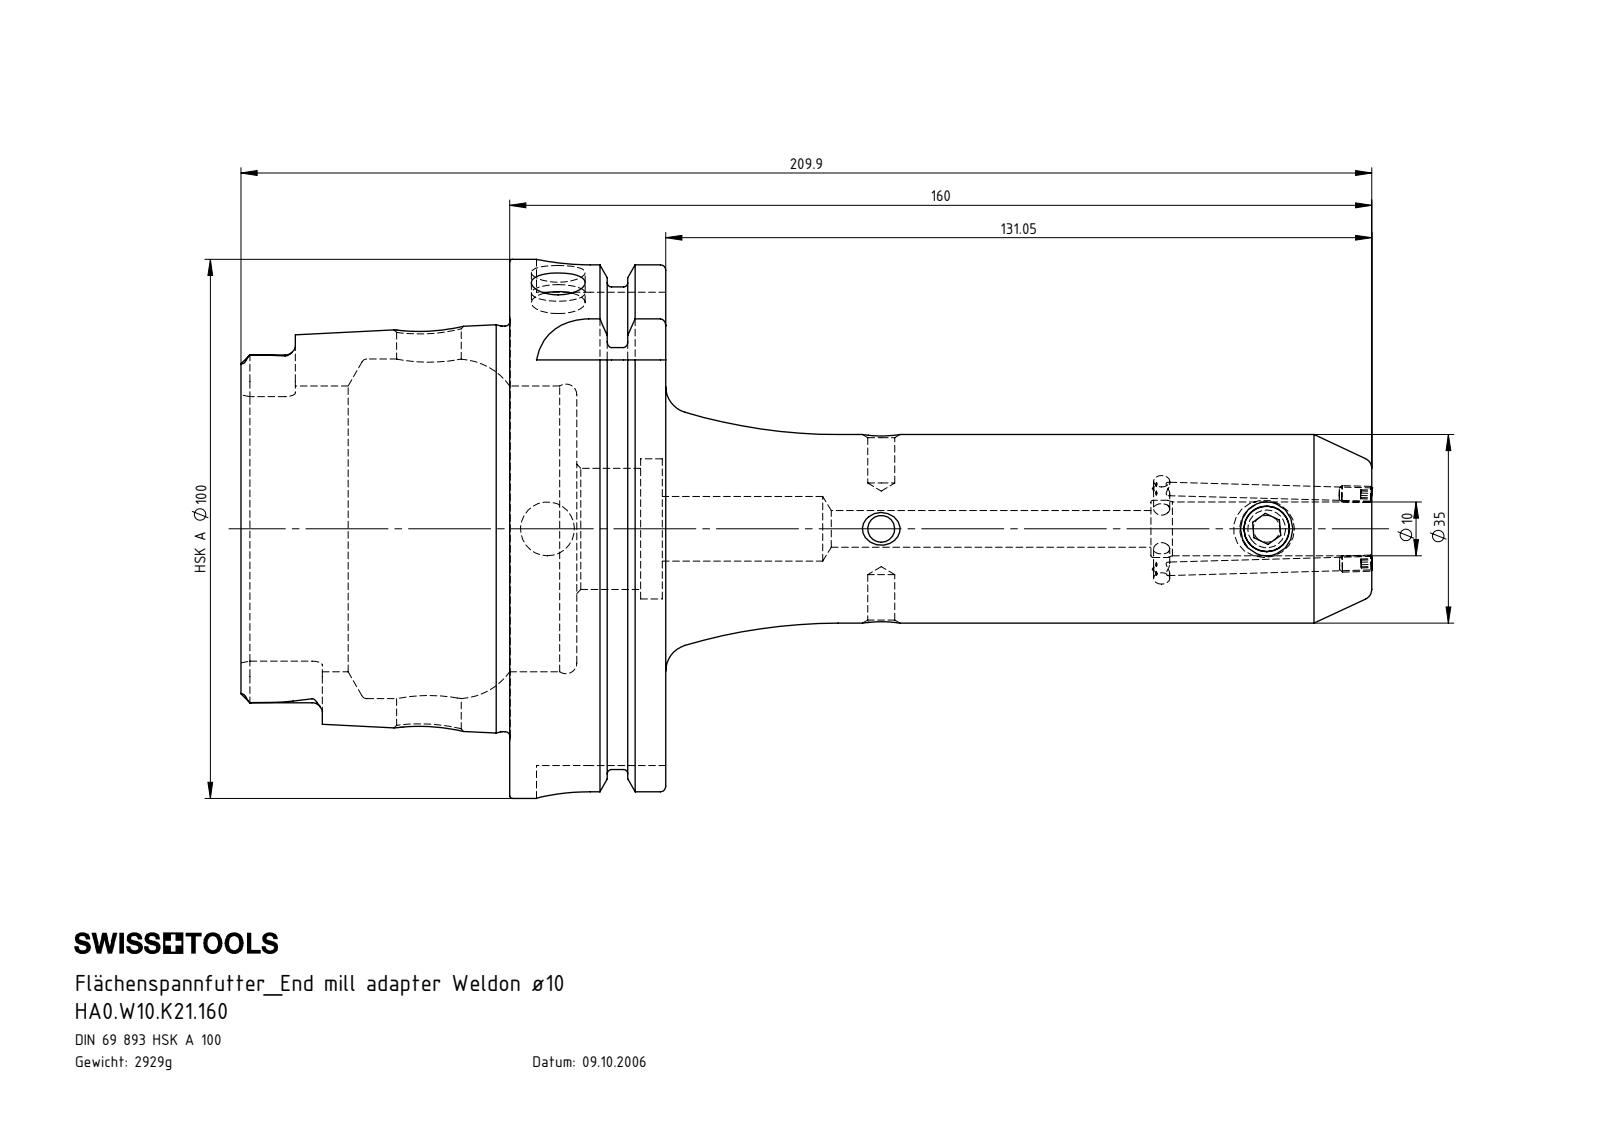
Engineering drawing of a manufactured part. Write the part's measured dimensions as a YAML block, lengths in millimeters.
part_name: "ERU-CJ2.001.006_Default; W10-ER1.001.012_Default; HA0.W10.K21.160; HA0-W10.K21.160_C_Fertigbearbeitung"
step_written_by: "SolidWorks 2009 (CONFIG_CONTROL_DESIGN)"
units: millimeters
bodies: {solids: 4, faces: 277, planar: 71, cylindrical: 84, other: 122}
overall_size: [209.98, 100, 100]
volume: 373085
surface_area: 69271
round_holes:
  - {diameter: 10, count: 4}
  - {diameter: 2.5, count: 2}
  - {diameter: 5, count: 2}
  - {diameter: 12, count: 2}
  - {diameter: 3, count: 1}
  - {diameter: 6.8, count: 1}
  - {diameter: 8.5, count: 1}
  - {diameter: 10.6, count: 1}
  - {diameter: 22.5, count: 1}
  - {diameter: 26, count: 1}
  - {diameter: 53, count: 1}
  - {diameter: 63, count: 1}
round_bosses_or_shafts:
  - {diameter: 3, count: 2}
  - {diameter: 100, count: 1}
  - {diameter: 91.95, count: 1}
  - {diameter: 75.26, count: 1}
  - {diameter: 35, count: 1}
  - {diameter: 10, count: 1}
partial_cylinders:
  - {radius: 1.9, count: 6}
  - {radius: 4.88, count: 4}
  - {radius: 10, count: 4}
face_to_face_distances: [28.95, 12.45, 16.5, 49.9, 62.35, 78.85, 87.8, 78.2, 28.3, 15.85]
hole_center_spacings: [61.95, 71.55, 83.95, 133.5]
